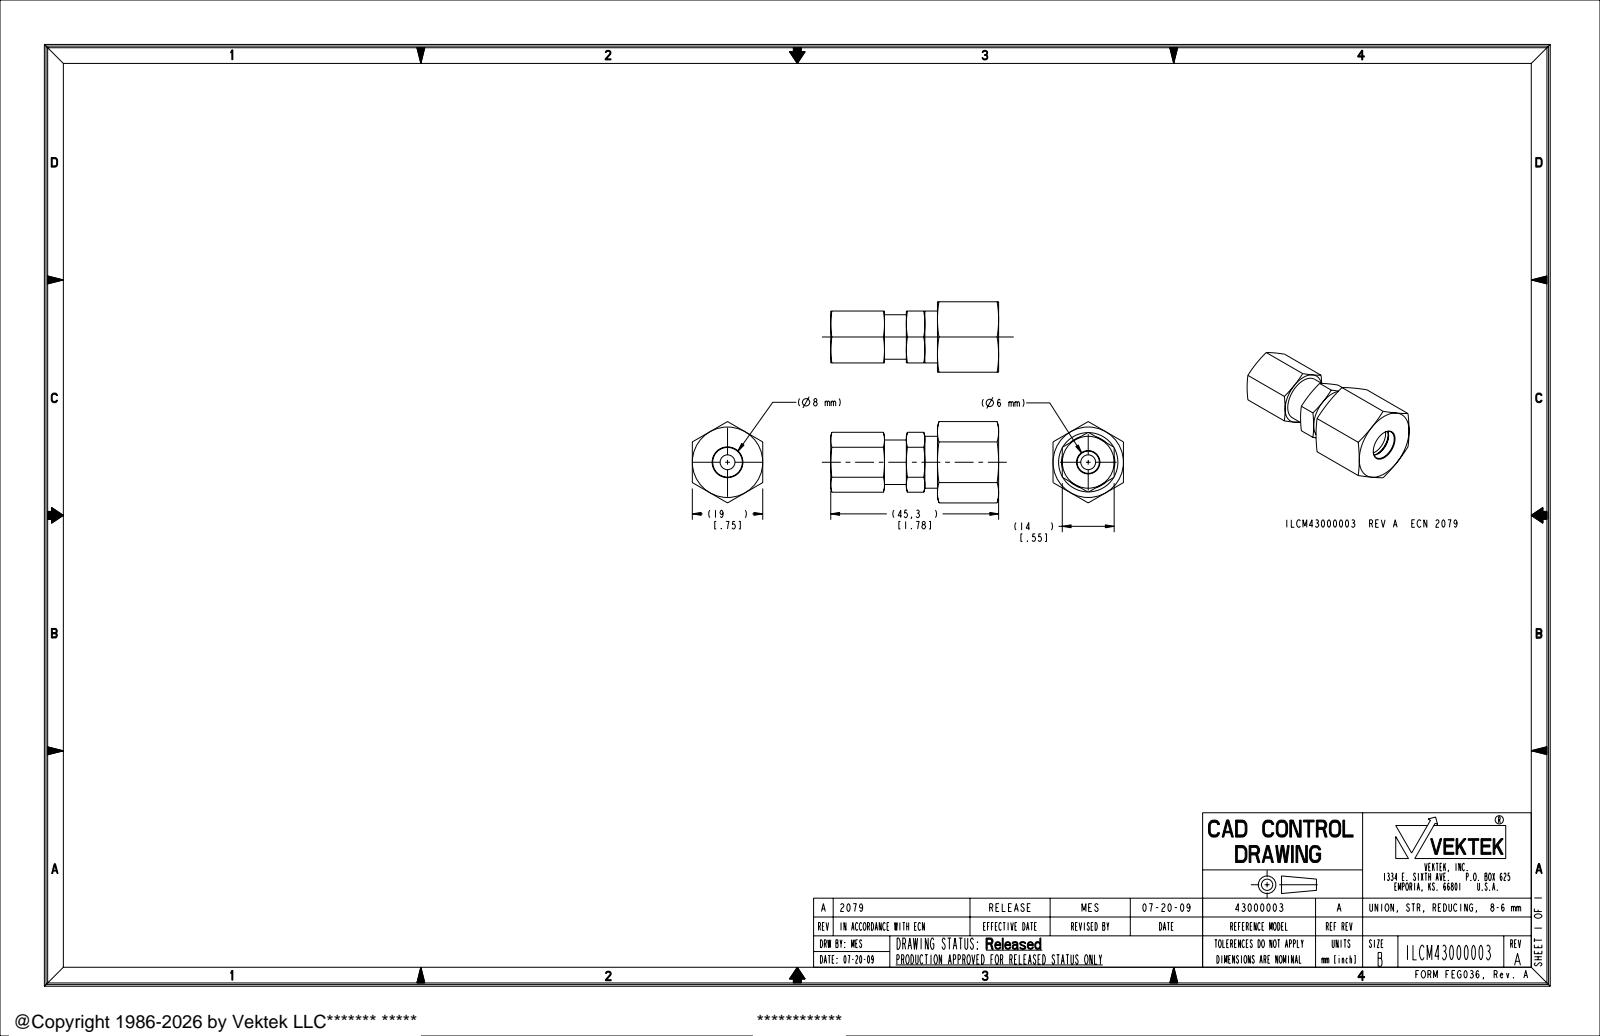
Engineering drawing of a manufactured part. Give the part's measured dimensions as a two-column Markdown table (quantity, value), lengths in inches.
| quantity | value |
| --- | --- |
| part name | ILCM43000003 |
| STEP written by | PRO/ENGINEER BY PARAMETRIC TECHNOLOGY CORPORATION, 2007460 (AUTOMOTIVE_DESIGN_CC2) |
| units | inches |
| bodies | 1 solid, 116 faces (30 planar, 24 cylindrical, 62 other) |
| overall size | 1.783 × 0.864 × 0.748 |
| volume | 0.44 in³ |
| surface area | 8.268 in² |
| round holes (diameter × count) | 0.157 × 1, 0.236 × 1, 0.315 × 1, 0.409 × 1, 0.566 × 1 |
| round bosses / shafts (diameter × count) | 0.551 × 1, 0.472 × 1, 0.433 × 1, 0.398 × 1 |
| main face-to-face distances | 0.65, 0.098, 0.748, 0.551, 1.783, 1.134, 0.276, 0.709, 0.98, 1.213 |
